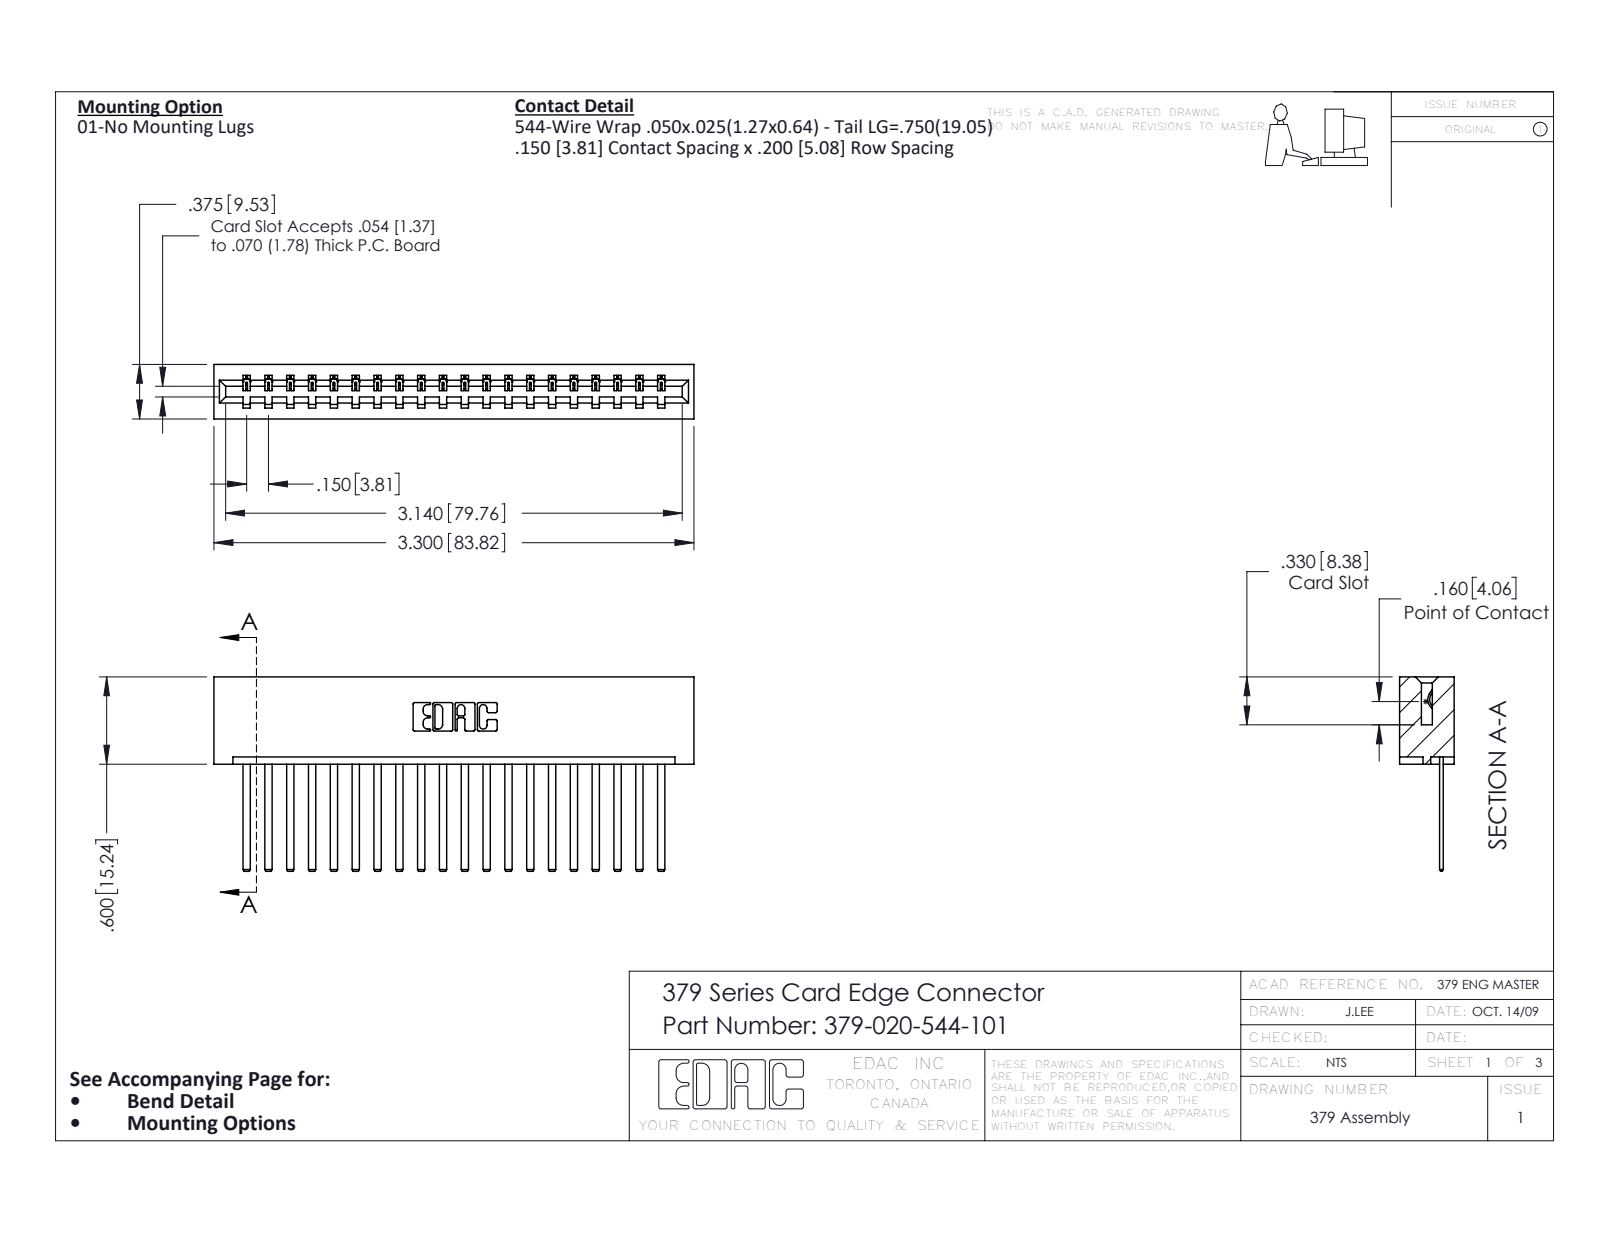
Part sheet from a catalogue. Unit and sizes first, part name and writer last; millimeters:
Units: millimetres
Overall size (bounding box): 83.8 × 34 × 9.5
Partial cylindrical surfaces — rounded edges, fillets, slot ends (radius × count): R0.2 ×40, R0.3 ×22, R0.2 ×6, R0.8 ×6, R0.7 ×3, R0.4 ×1, R0.6 ×1, R0.6 ×1
Main face-to-face distances: 7.6, 1.9, 9.5, 3.8, 15.2, 2.5, 7, 0.6, 11.4, 5.7
Volume: 9 490 mm³ · Surface area: 10 340 mm²
Bodies: 21 solids, 1146 faces (826 planar, 320 cylindrical, 0 other)
Part name (STEP PRODUCT): 379-020-544-101; 345-292-001_345-293-144; 379 Part_Lugless
STEP written by: SolidWorks 2016 (CONFIG_CONTROL_DESIGN)
